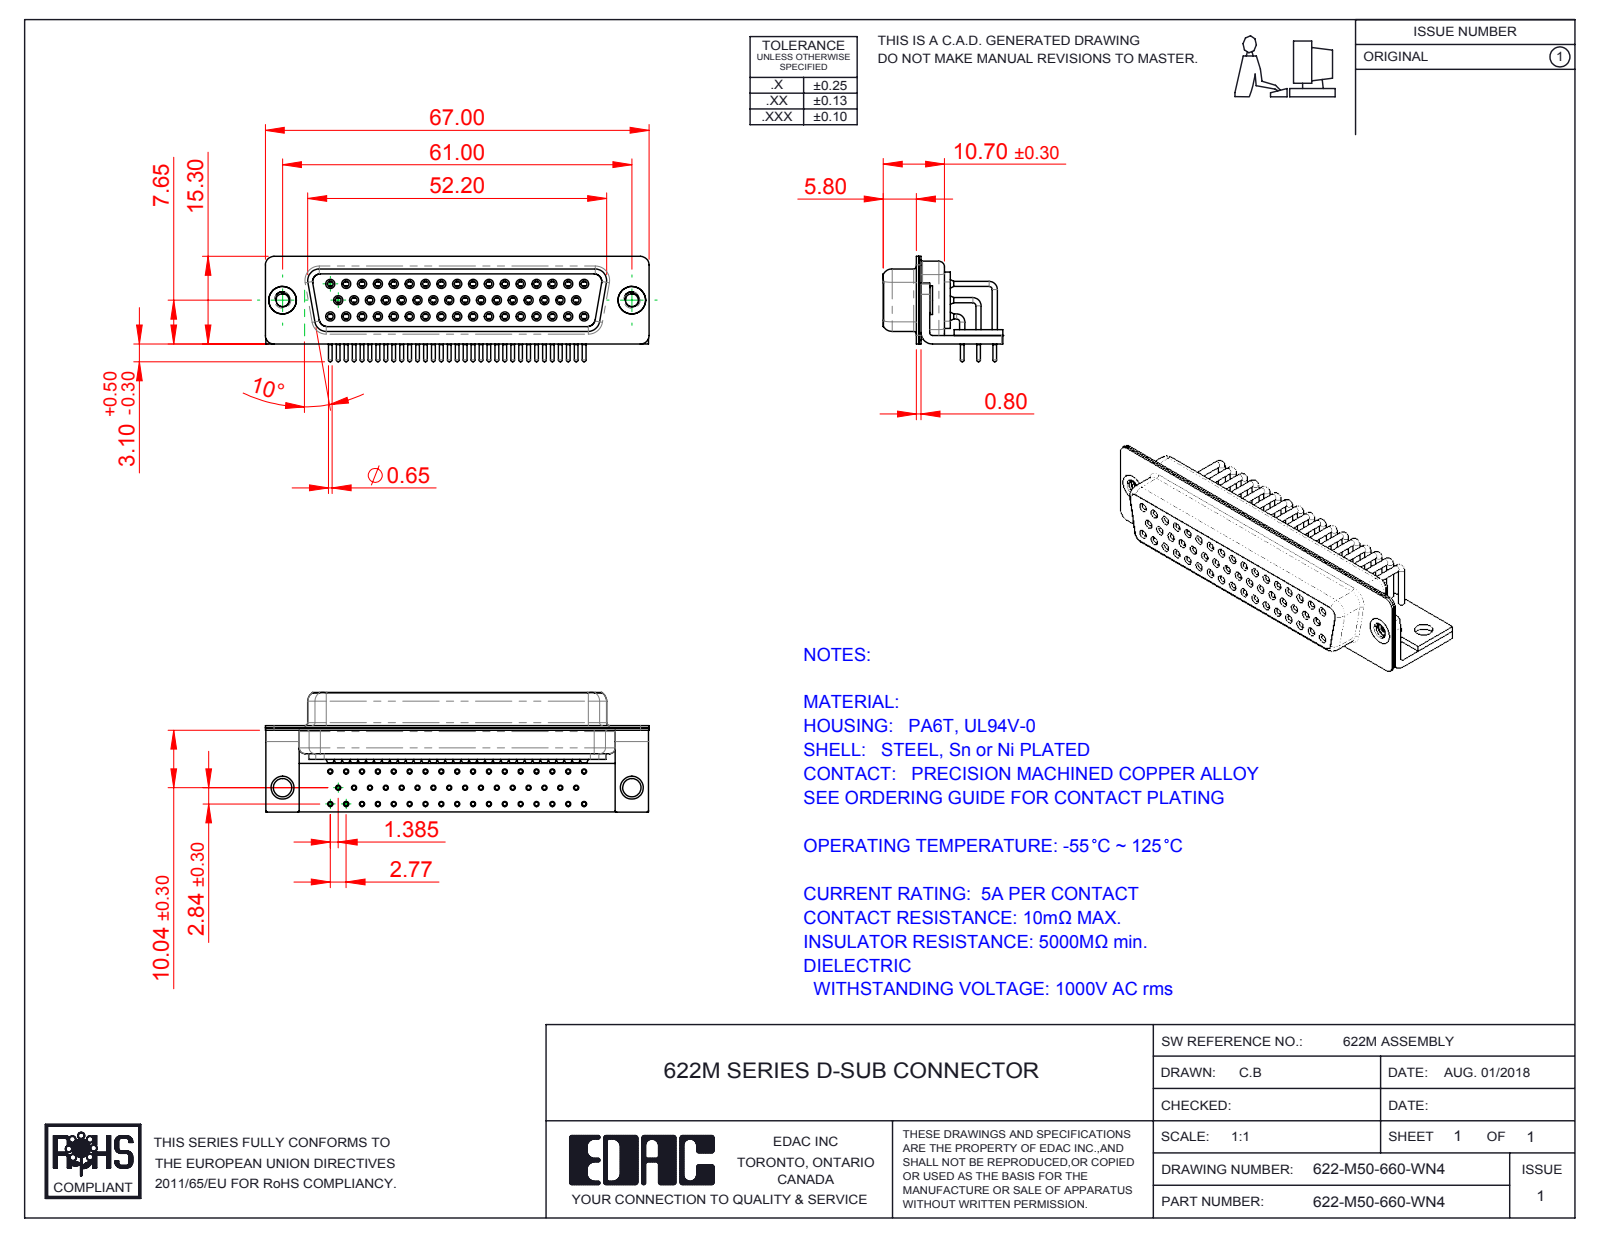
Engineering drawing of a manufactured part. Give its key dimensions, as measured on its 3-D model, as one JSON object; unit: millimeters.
{"part_name": "622M Housing_50 Contacts; 622M Shell Front_50 Contacts; 622M Shell Rear_50 Contacts; 622M 4-40 Threaded Rivet_Stabilizer (+6 more)", "step_written_by": "SolidWorks 2016 (CONFIG_CONTROL_DESIGN)", "units": "millimeters", "bodies": {"solids": 58, "faces": 3079, "planar": 843, "cylindrical": 1409, "other": 827}, "overall_size": [67, 20.9, 18.4], "volume_mm3": 7744, "surface_area_mm2": 18114, "round_holes": [[0.9, 50], [1, 50], [1.1, 50], [1.7, 50], [1.8, 50], [2, 50], [2.26, 2], [3.2, 2], [4, 2], [4.8, 2]], "round_bosses_or_shafts": [[0.9, 59], [1.6, 50], [1.5, 50], [0.65, 50], [5, 2], [4.9, 2]], "partial_cylinders_radius": [[0.25, 16], [1.5, 16], [2, 13], [1.35, 8], [1.6, 8], [0.5, 5], [0.6, 4], [0.65, 4]], "face_to_face_distances": [0.4, 1, 2.2, 0.85, 1.35, 11.85, 12.25, 5.8, 5.9, 0.8], "hole_center_spacings": [2.77, 3.16, 5.54, 8.31, 11.08, 13.85, 16.62, 19.39]}
